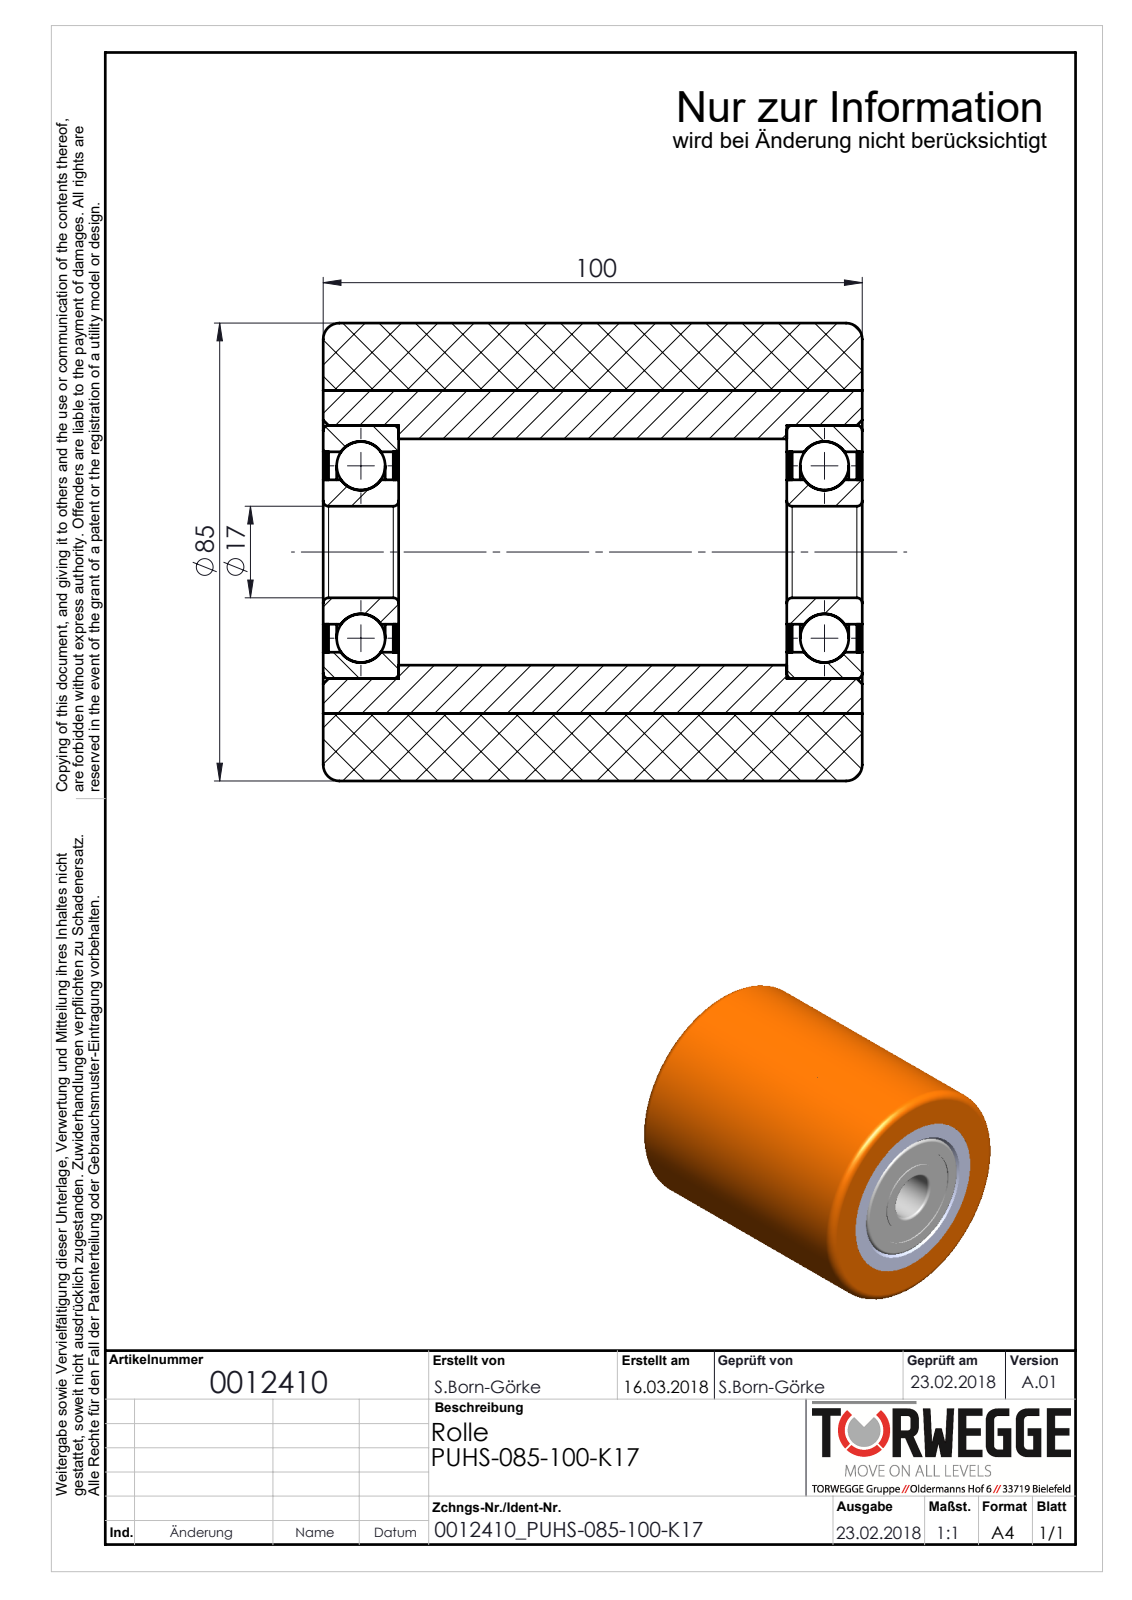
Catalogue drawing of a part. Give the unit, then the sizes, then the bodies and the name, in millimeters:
Units: millimetres
Overall size (bounding box): 100 × 85 × 85
Round holes (diameter × count): ⌀17 ×1, ⌀26.8 ×1, ⌀37.2 ×1, ⌀42 ×1, ⌀47 ×1, ⌀60 ×1
Round bosses / shafts (diameter × count): ⌀85 ×1
Main face-to-face distances: 86, 0.5, 100, 13, 14, 1, 13.5, 86.5, 12.5, 85.5
Volume: 454 917 mm³ · Surface area: 111 410 mm²
Bodies: 12 solids, 118 faces (22 planar, 52 cylindrical, 44 other)
Part name (STEP PRODUCT): 0012410_PUHS-085-100-K17
STEP written by: SolidWorks 2016 (AUTOMOTIVE_DESIGN)
